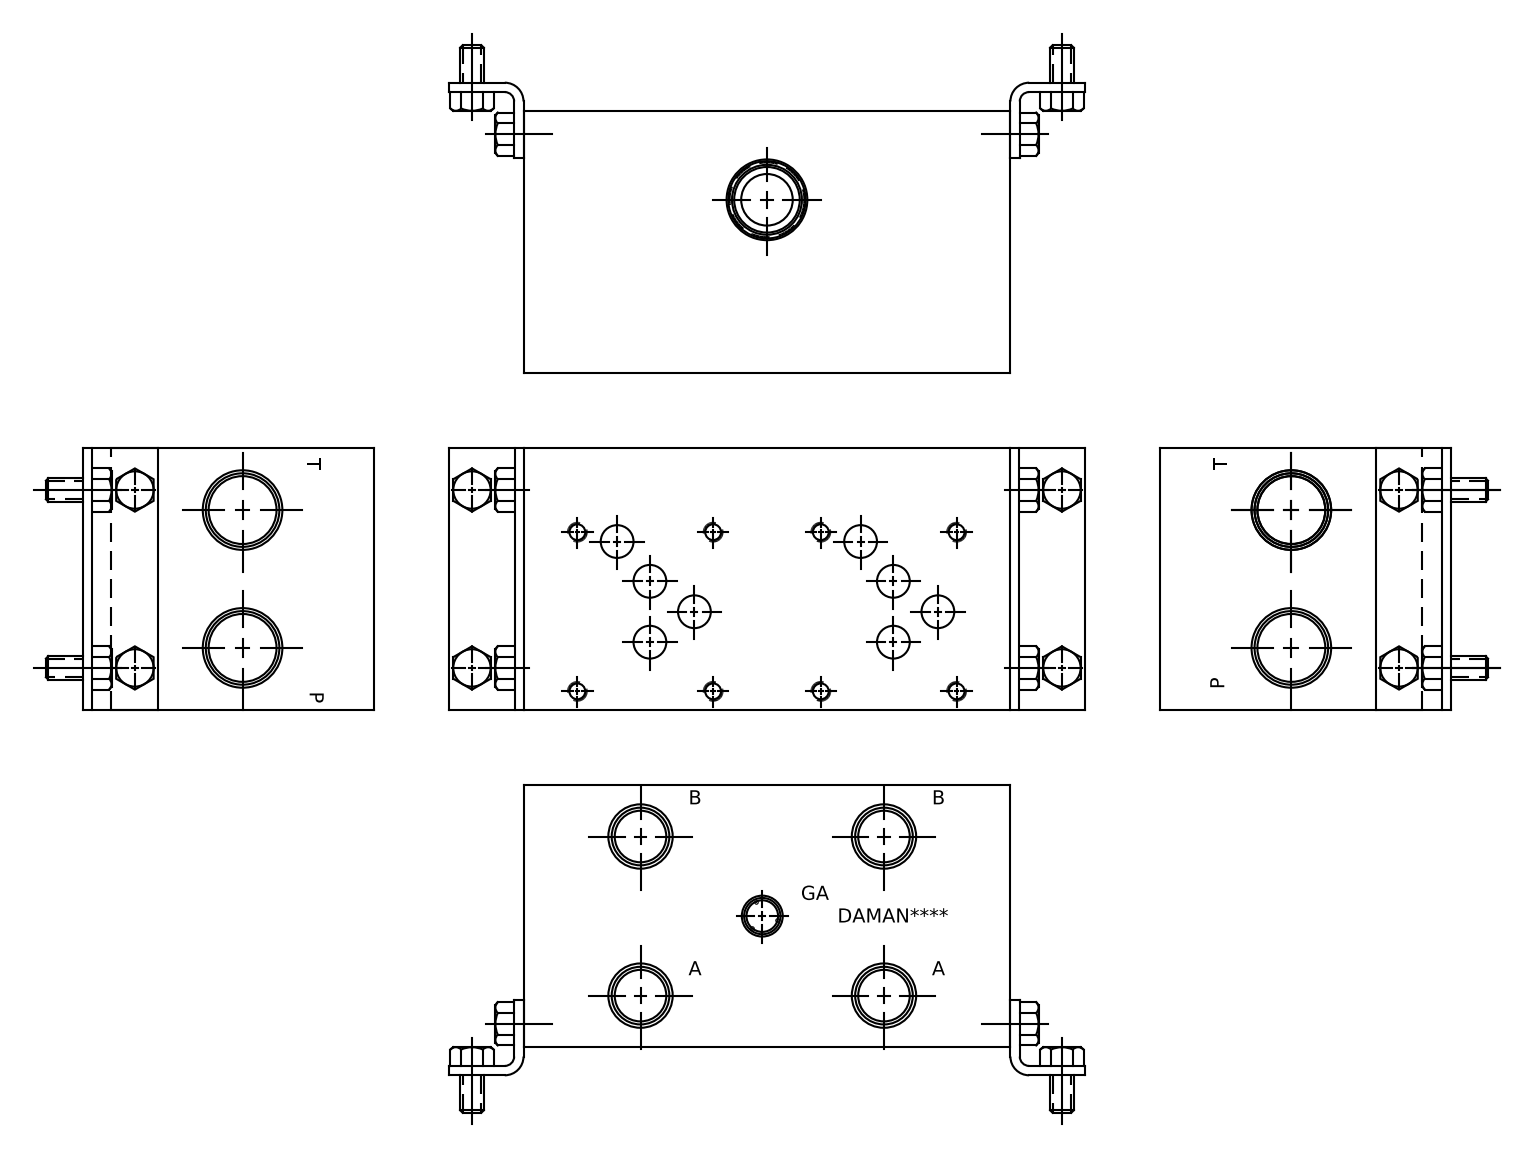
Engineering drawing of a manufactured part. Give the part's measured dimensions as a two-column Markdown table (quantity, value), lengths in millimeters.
| quantity | value |
| --- | --- |
| part name | D05P023P_S |
| STEP written by | Autodesk Inventor 2021 (AUTOMOTIVE_DESIGN) |
| units | millimeters |
| bodies | 1 solid, 622 faces (361 planar, 56 cylindrical, 205 other) |
| overall size | 165.1 × 88.9 × 88.9 |
| volume | 1 202 000 mm³ |
| surface area | 95 347 mm² |
| round holes (diameter × count) | 5.11 × 8, 6.35 × 8, 11.13 × 7, 17.48 × 5, 21.59 × 4, 6.53 × 2, 7.92 × 2, 23.01 × 2, 26.92 × 2, 10.72 × 1, 11.11 × 1, 13.87 × 1 |
| main face-to-face distances | 88.9, 165.1, 15.85, 149.25, 15.37, 73.53, 133.4, 15.33, 88.86, 40.13 |
| hole center spacings | 82.55, 46.05, 70.95, 53.98, 98.63, 13.88, 18.27, 27.13 |
